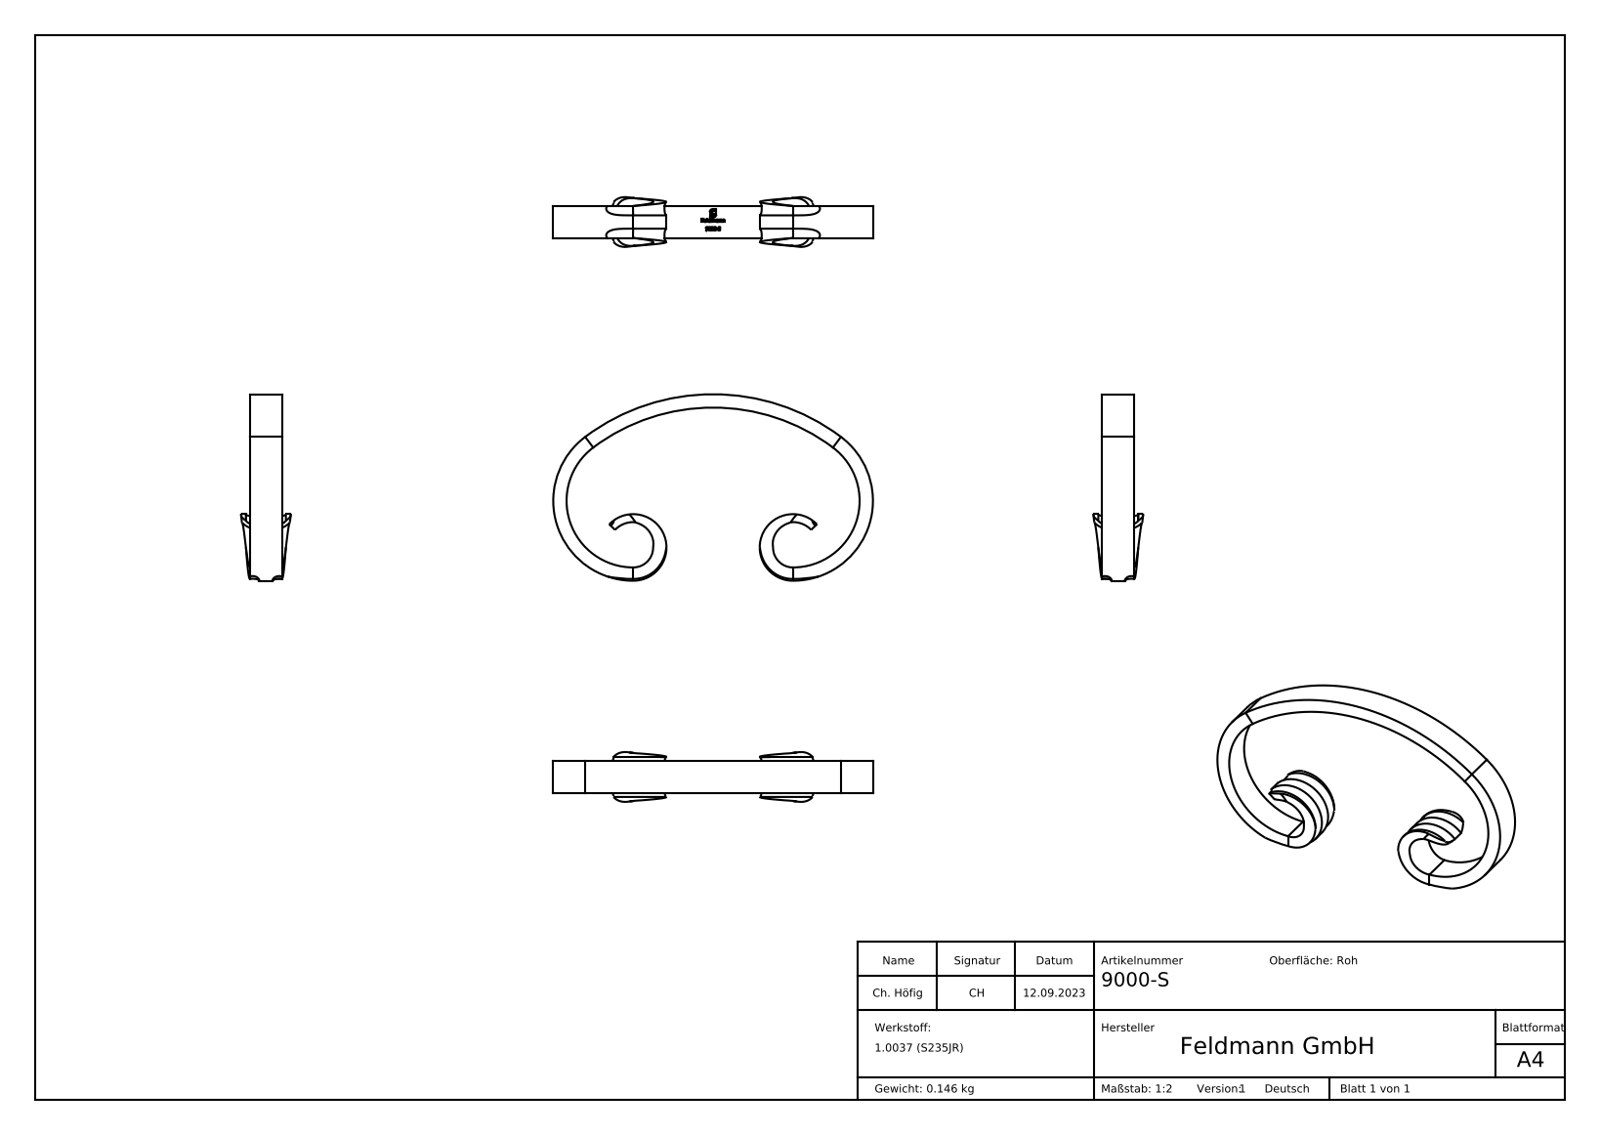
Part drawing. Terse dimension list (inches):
name: 9000-S
written by: SolidWorks 2018 (CONFIG_CONTROL_DESIGN)
unit: in
bodies: 1 solid, 264 faces (93 planar, 28 cylindrical, 143 other)
size: 4.724 × 2.756 × 0.736
volume: 1.145 in³; area: 17.53 in²
rounds: 2× R0.984, 2× R1.181, 1× R2.953, 1× R2.957, 1× R3.15
face distances: 0.472, 0.045, 0.133, 0.013, 0.236, 0.112, 0.015, 0.072, 0.013, 0.117
